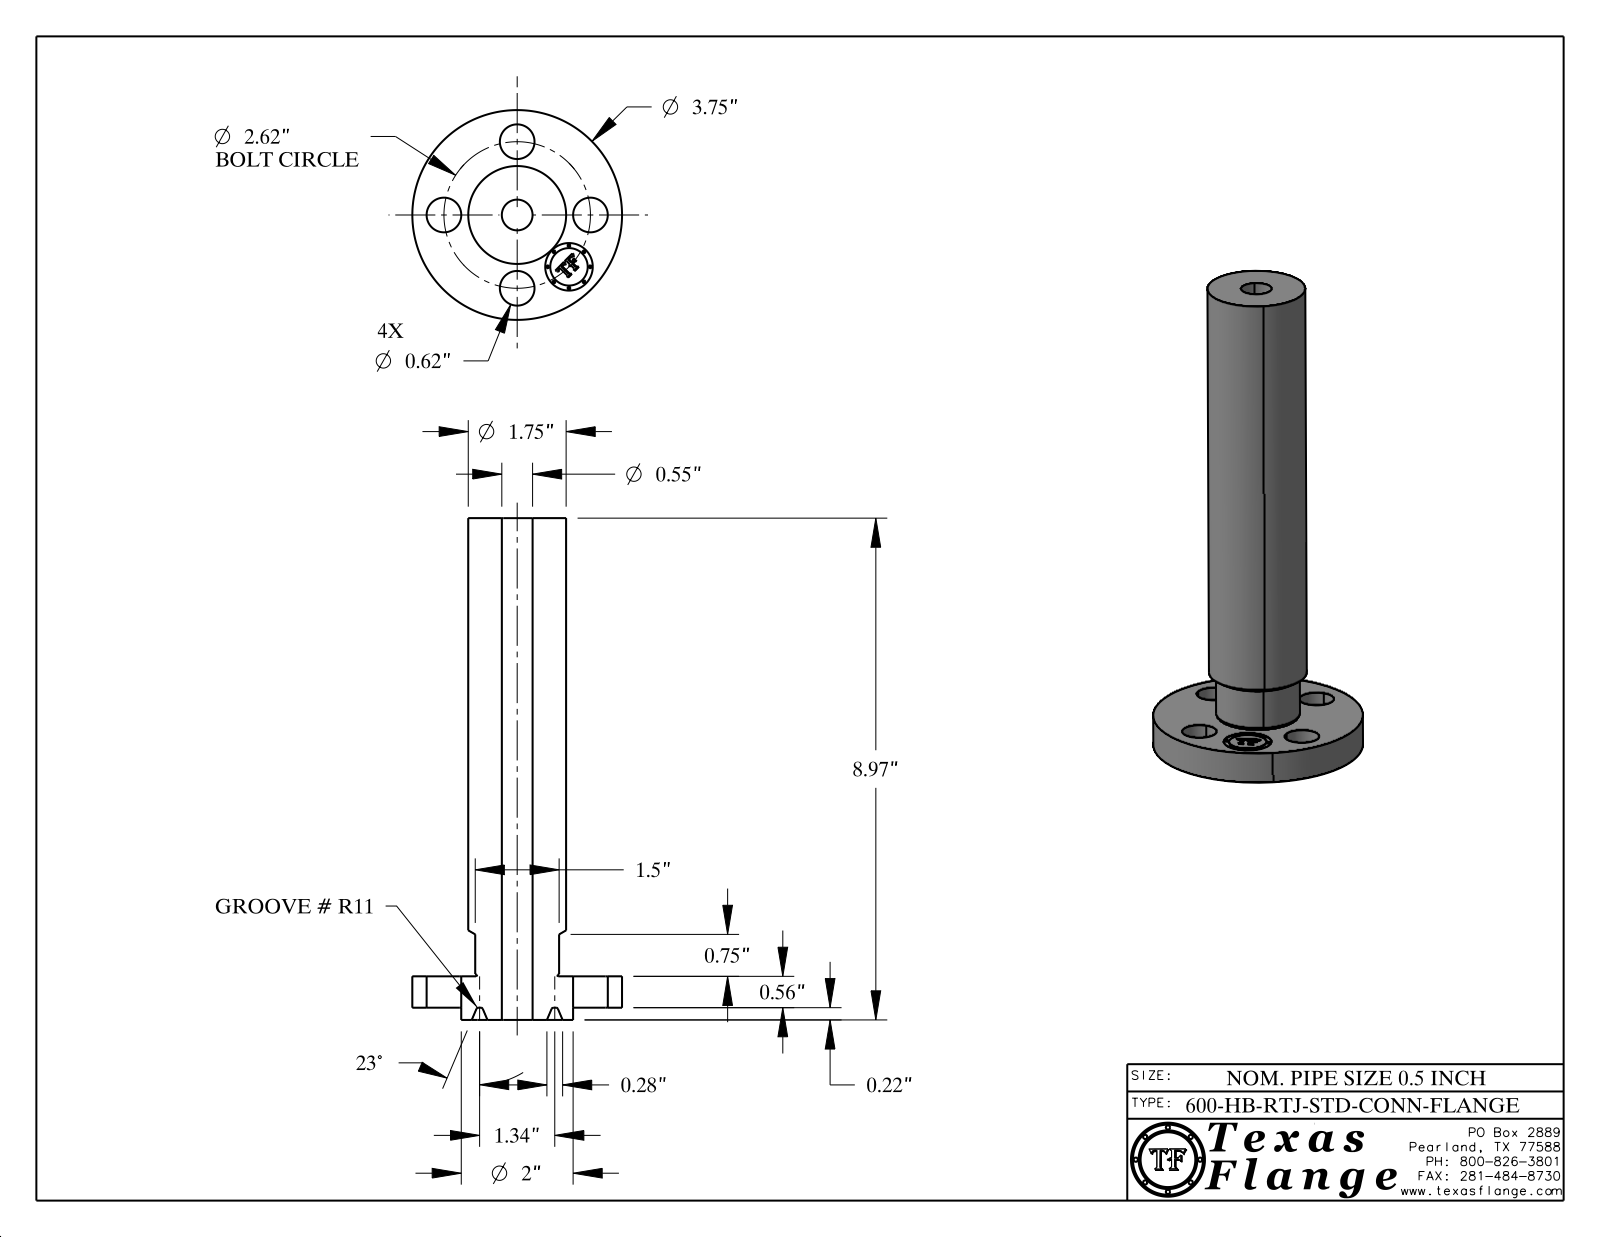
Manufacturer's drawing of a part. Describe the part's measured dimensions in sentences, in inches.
The part is named "0.5-600-HB-RTJ-STD-CONN-FLANGE". Its 3-D file was written by "CATIA V5 STEP AP214 (AUTOMOTIVE_DESIGN)". It is 1 solid with 423 faces: 371 planar, 38 cylindrical and 14 other. Overall it measures 8.969 by 3.75 by 3.75 inches. Its volume is 23.08 cubic inches and its surface area 93.86 square inches. Round holes: 4 of diameter 0.62, 1 of diameter 0.55, 1 of diameter 0.85. Round bosses or shafts: 8 of diameter 0.051, 1 of diameter 3.75, 1 of diameter 2, 1 of diameter 1.75, 1 of diameter 1.5, 1 of diameter 0.67. The main face-to-face distances are 0.56, 8.75, 8.19, 0.219, 0.779, 8.969, 0.774, 0.555, 8.195, 0.254. The hole center spacings are 1.31, 1.852, 1.003, 2.42, 2.62, 1.31.
